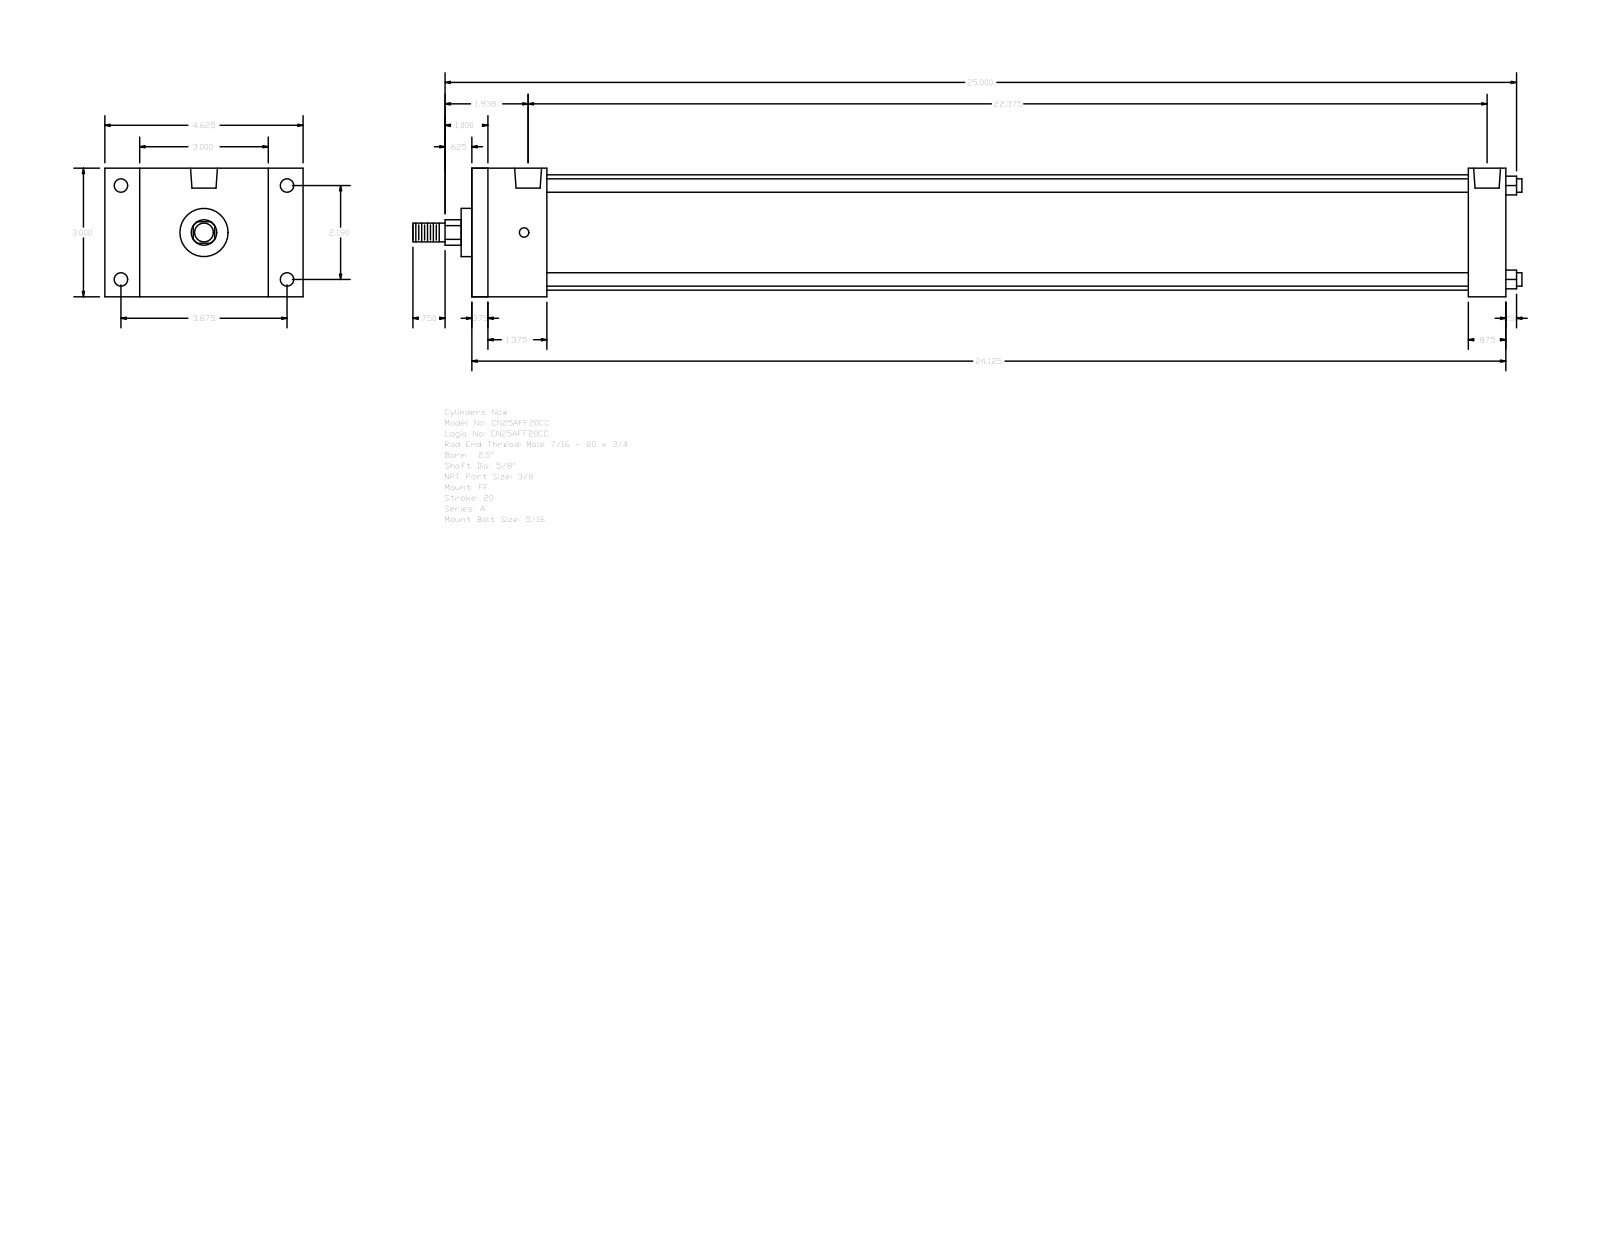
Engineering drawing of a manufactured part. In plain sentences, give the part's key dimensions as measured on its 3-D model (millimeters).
The part is named "A_FF__0250_0.625". Its 3-D file was written by "GSSL Pune (CONFIG_CONTROL_DESIGN)". It is 0 solids with 92 faces: 64 planar, 28 cylindrical and 0 other. Overall it measures 657.23 by 117.47 by 76.2 millimeters. Round holes: 4 of diameter 5.56, 4 of diameter 7.94, 2 of diameter 15.93. Round bosses or shafts: 4 of diameter 7.94, 1 of diameter 68.33, 1 of diameter 28.57, 1 of diameter 15.88, 1 of diameter 11.11. Partial cylindrical surfaces (rounded edges, fillets, slot ends): 1 of radius 7.54. The main face-to-face distances are 76.2, 612.77, 9.52, 603.25, 44.45, 34.93, 590.54, 581.02, 546.09, 568.32. The hole center spacings are 2.38, 55.62, 98.42, 113.05, 570.71, 573.09, 568.33.
